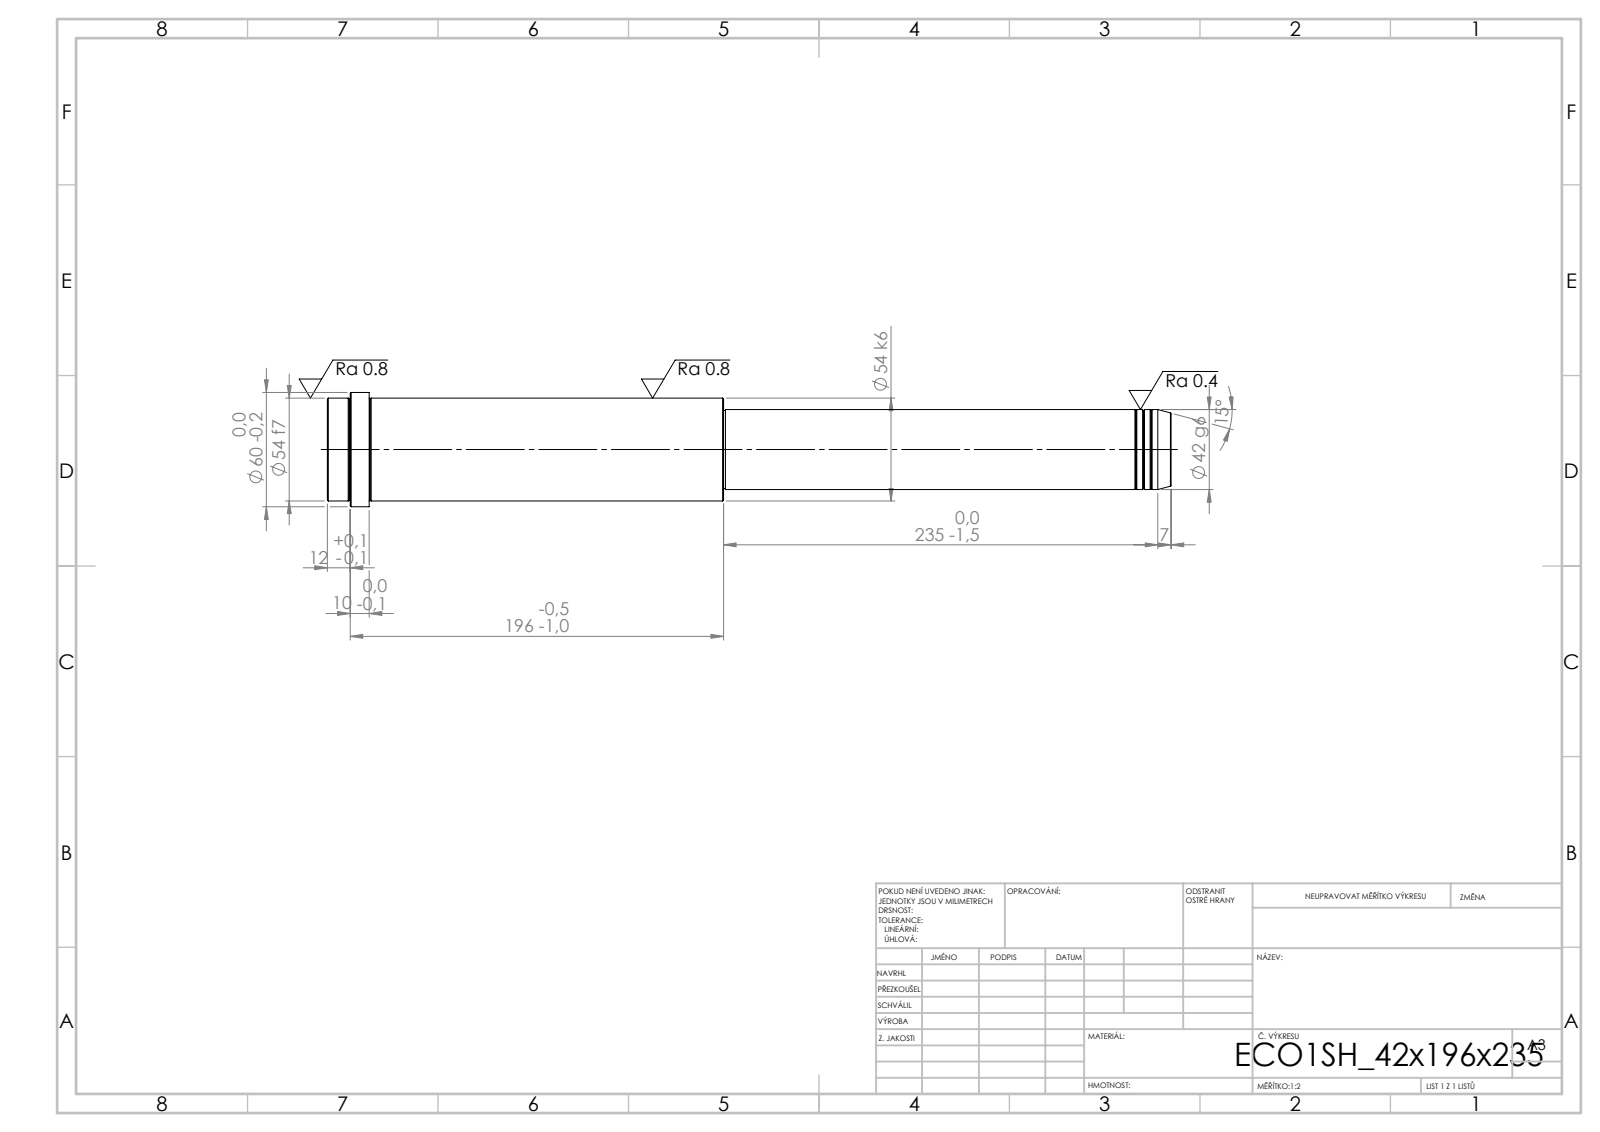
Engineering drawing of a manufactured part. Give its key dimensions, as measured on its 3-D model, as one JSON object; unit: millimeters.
{"step_written_by": "SolidWorks 2019 (CONFIG_CONTROL_DESIGN)", "units": "millimeters", "bodies": {"solids": 1, "faces": 52, "planar": 6, "cylindrical": 16, "other": 30}, "overall_size": [443, 60, 60], "volume_mm3": 806056, "surface_area_mm2": 72253, "round_bosses_or_shafts": [[60, 1], [54, 1], [42, 1], [41, 1]], "face_to_face_distances": [443, 235, 208, 421, 186, 22, 431, 196, 10, 12]}
